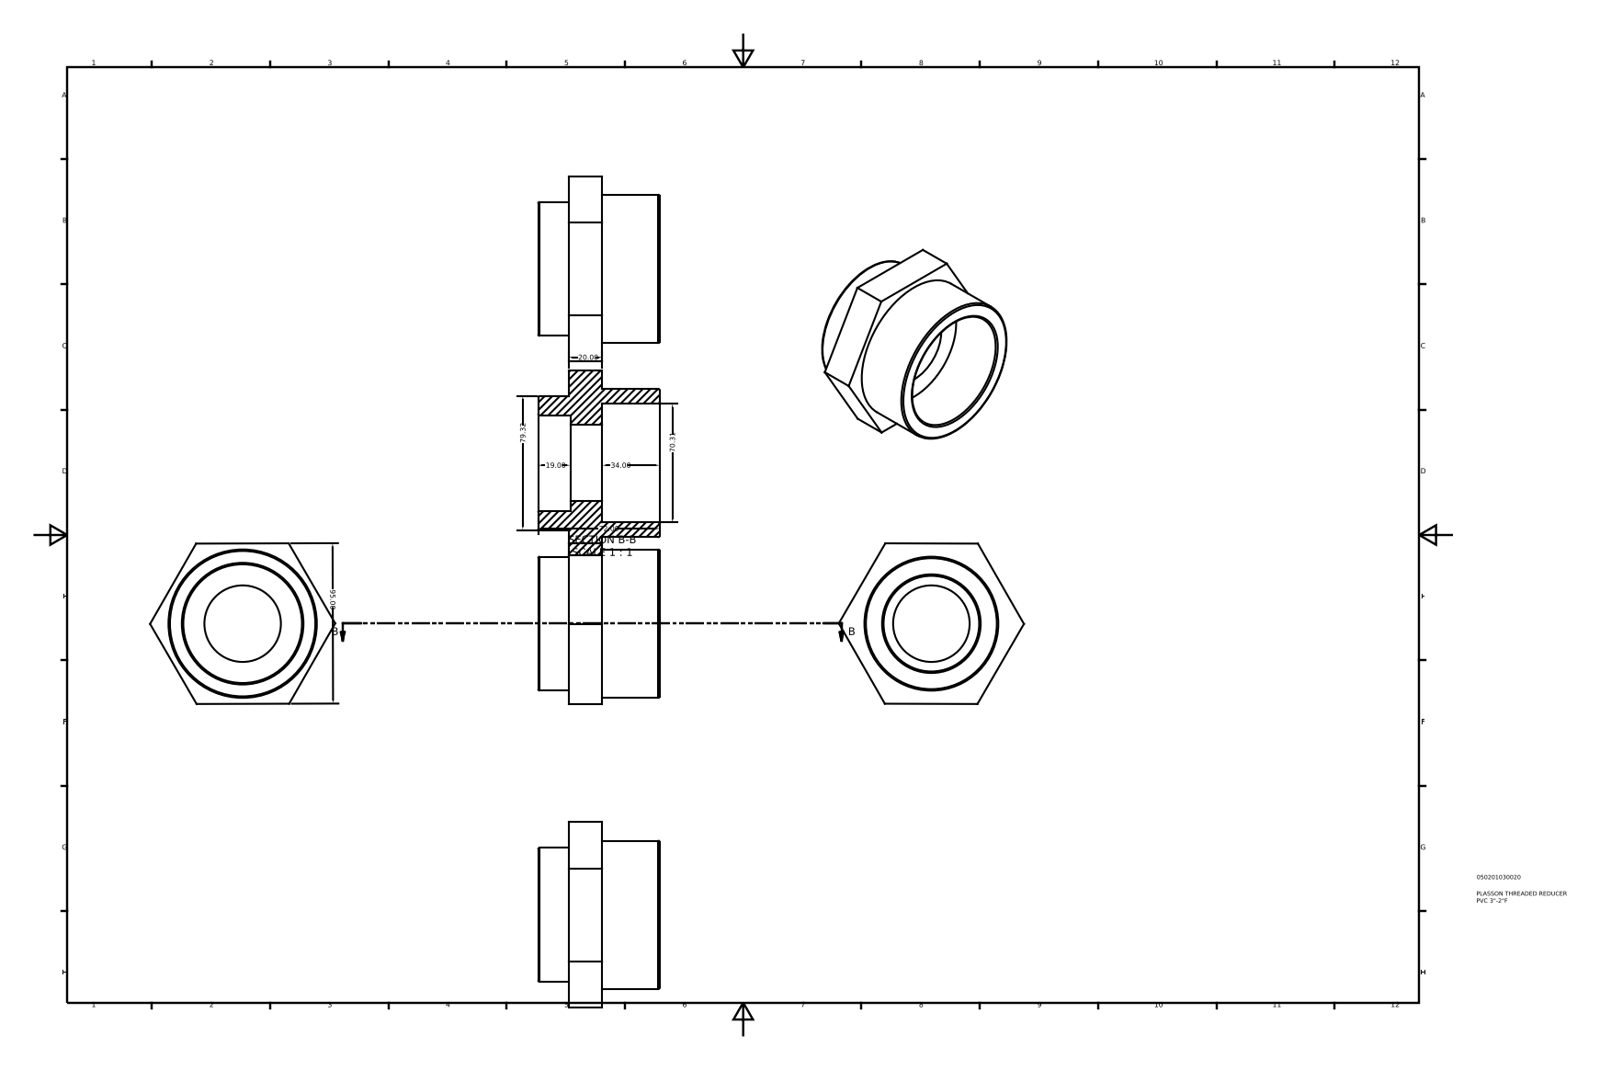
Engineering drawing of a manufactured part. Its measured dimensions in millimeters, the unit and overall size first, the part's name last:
Units: millimetres
Overall size (bounding box): 109.7 × 95.16 × 72
Round holes (diameter × count): ⌀45.32 ×1, ⌀56.66 ×1, ⌀70.31 ×1
Round bosses / shafts (diameter × count): ⌀87.88 ×1, ⌀79.32 ×1
Main face-to-face distances: 20, 95.06, 18, 38, 19, 72, 54, 34, 95, 1
Volume: 240 800 mm³ · Surface area: 46 108 mm²
Bodies: 1 solid, 21 faces (12 planar, 5 cylindrical, 4 other)
Part name (STEP PRODUCT): 050201030020
STEP written by: Autodesk Inventor 2015 (AUTOMOTIVE_DESIGN)
